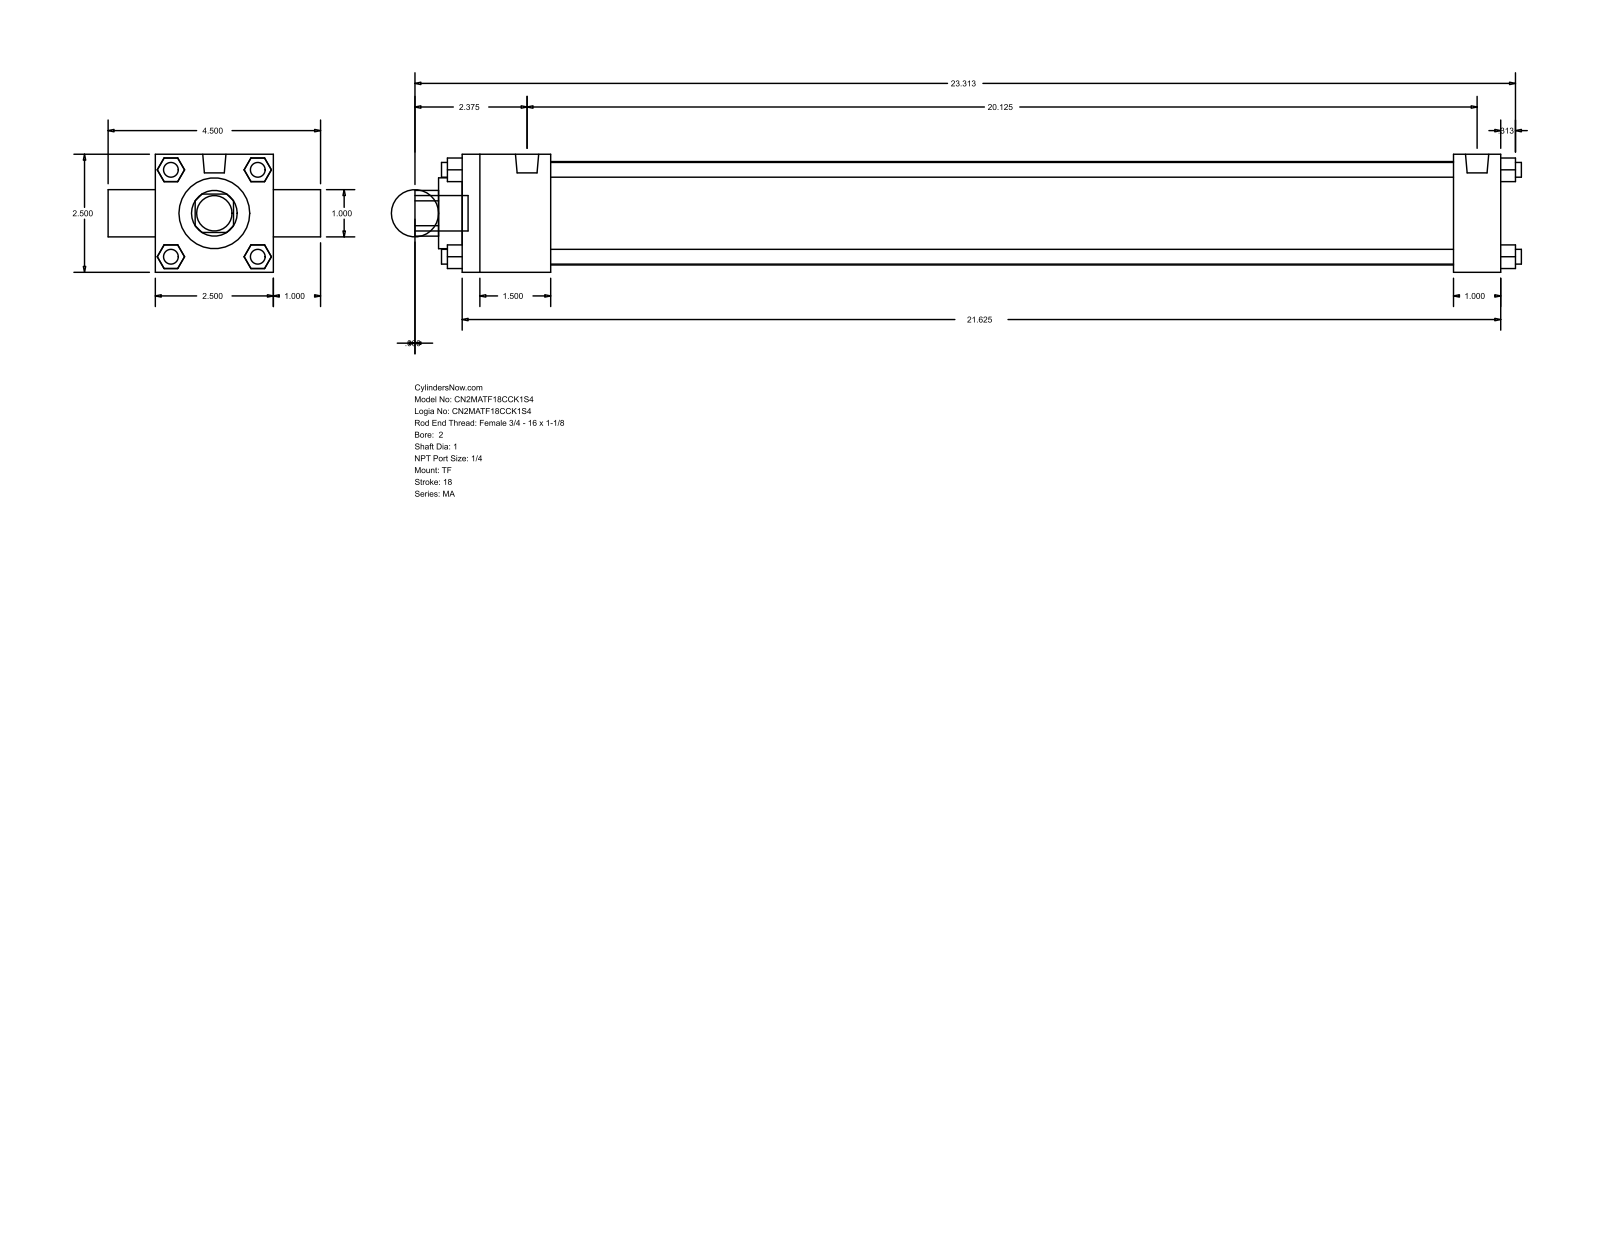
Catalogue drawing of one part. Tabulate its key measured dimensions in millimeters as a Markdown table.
| quantity | value |
| --- | --- |
| part name | MA_TF__0200_1 |
| STEP written by | GSSL Pune (CONFIG_CONTROL_DESIGN) |
| units | millimeters |
| bodies | 0 solids, 120 faces (92 planar, 28 cylindrical, 0 other) |
| overall size | 595.31 × 114.3 × 63.5 |
| round holes (diameter × count) | 25.4 × 2, 38.1 × 1, 55.63 × 1 |
| round bosses / shafts (diameter × count) | 7.94 × 7, 12.49 × 2, 19.05 × 1 |
| partial cylindrical surfaces (radius × count) | 12.29 × 1 |
| main face-to-face distances | 63.5, 25.4, 558.8, 12.7, 47.63, 533.4, 485.77, 511.17, 88.9, 40.47 |
